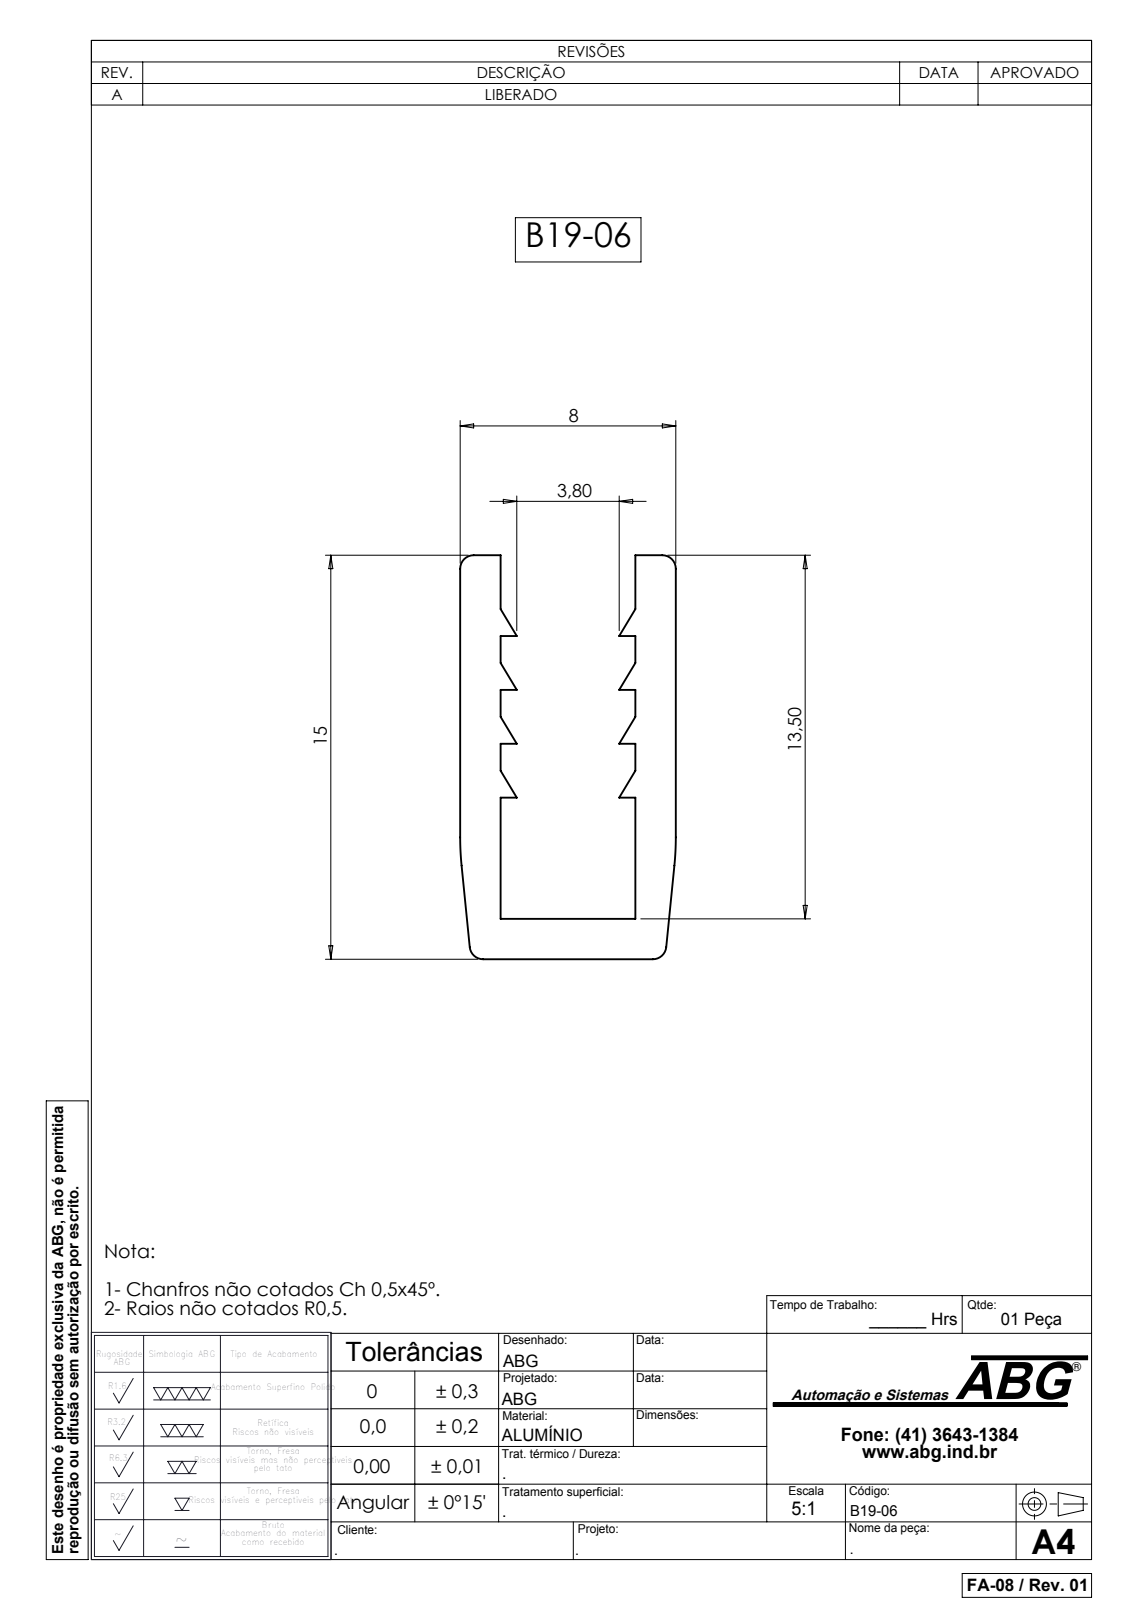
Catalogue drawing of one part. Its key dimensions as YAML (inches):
part_name: "B19-06"
step_written_by: "SolidWorks 2007 (CONFIG_CONTROL_DESIGN)"
units: inches
bodies: {solids: 1, faces: 42, planar: 36, cylindrical: 6, other: 0}
overall_size: [118.11, 0.591, 0.315]
volume: 9.721
surface_area: 361
partial_cylinders:
  - {radius: 0.02, count: 4}
  - {radius: 0.413, count: 2}
face_to_face_distances: [0.059, 0.256, 0.315, 0.197, 0.041, 0.079, 0.157, 0.236, 0.081, 0.081]
